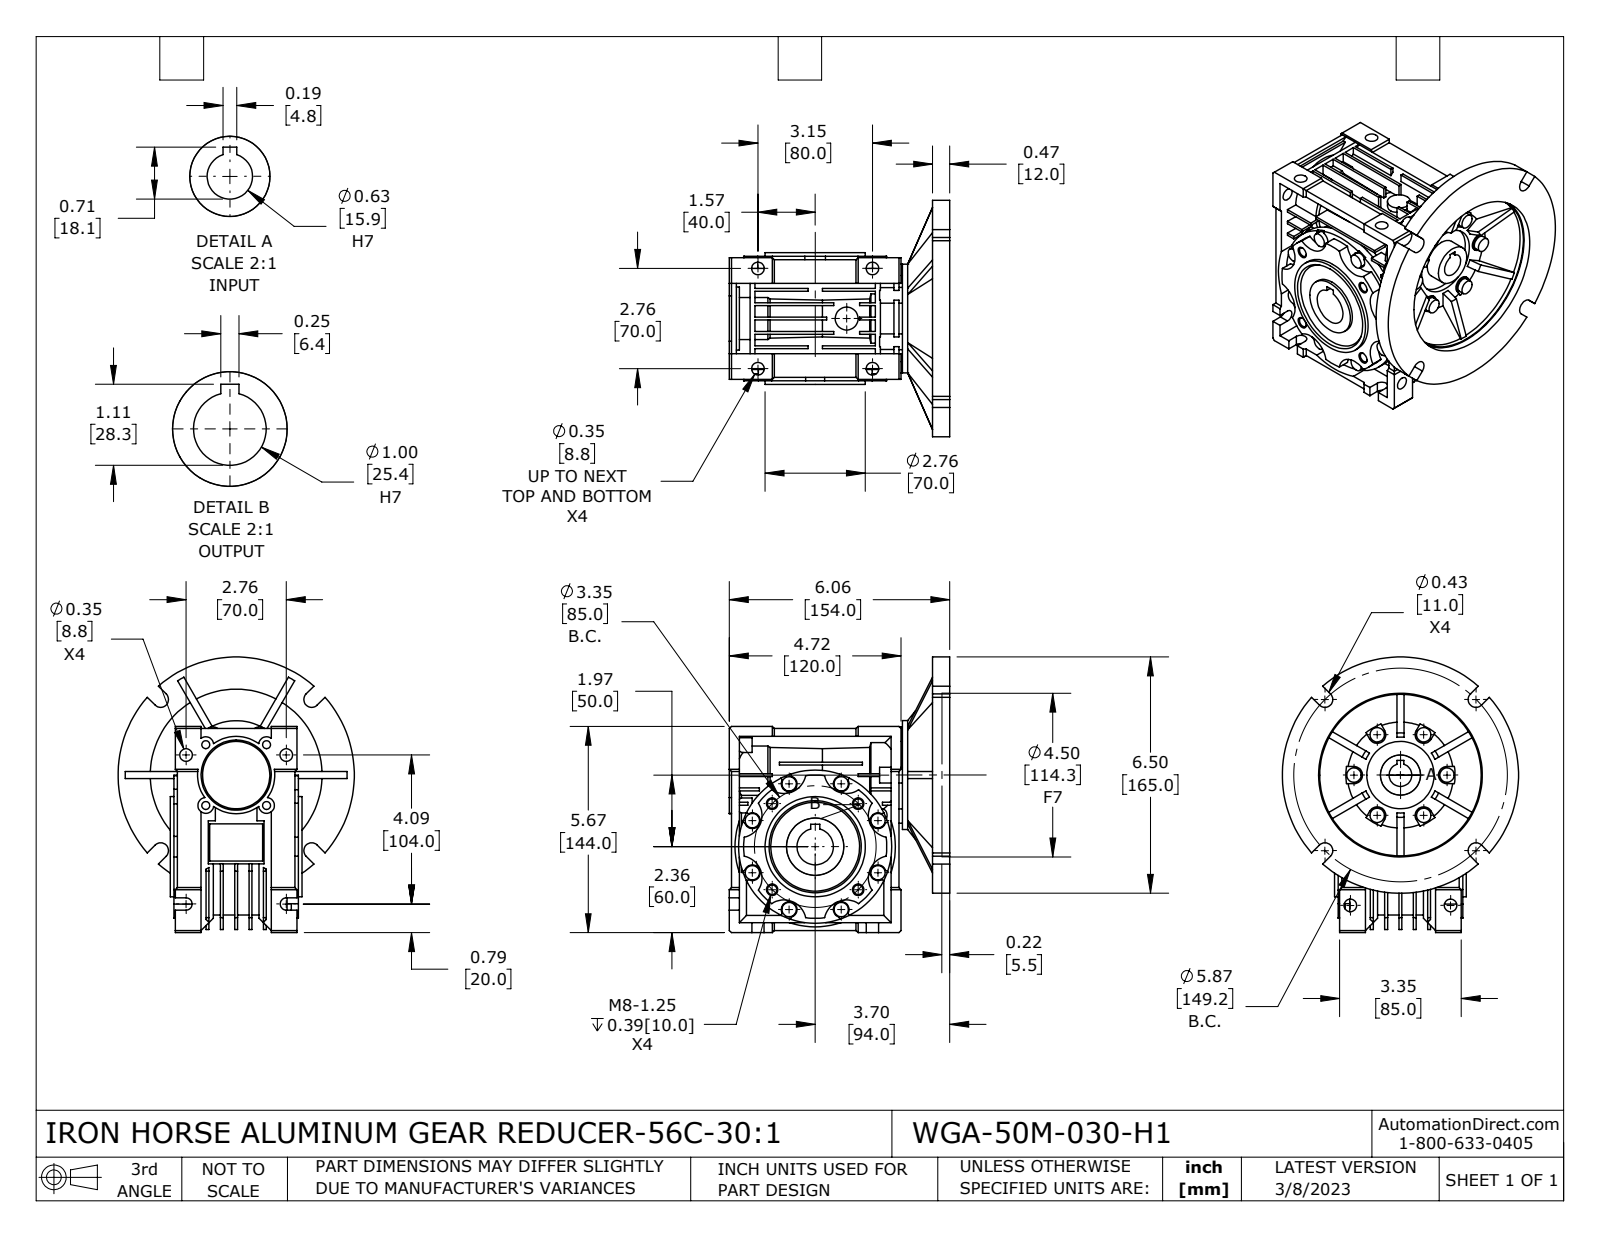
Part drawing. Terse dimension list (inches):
name: WGA-50M-030-H1
written by: SolidWorks 2021 (CONFIG_CONTROL_DESIGN)
unit: in
bodies: 4 solids, 954 faces (558 planar, 292 cylindrical, 104 other)
size: 7.579 × 6.496 × 6.063
volume: 72.69 in³; area: 412.5 in²
holes: 8× ⌀0.346, 4× ⌀0.219, 4× ⌀0.262, 2× ⌀0.262, 1× ⌀0.625, 1× ⌀0.65, 1× ⌀1, 1× ⌀1.102, 1× ⌀1.339, 1× ⌀1.575, 1× ⌀1.85, 1× ⌀4.441
bosses: 14× ⌀0.394, 1× ⌀6.496, 1× ⌀4.213, 1× ⌀2.992, 1× ⌀2.756, 1× ⌀2.402, 1× ⌀2.165, 1× ⌀2.126
rounds: 22× R0.217, 14× R0.236, 8× R0.591, 8× R0.61, 6× R0.167, 1× R1.811, 1× R1.878, 1× R1.969
face distances: 0.472, 0.394, 0.079, 0.276, 0.315, 0.059, 0.217, 0.787, 2.165, 1.378
hole spacings: 1.181, 1.67, 1.673, 2.366, 2.756, 0.613, 1.484, 1.489
